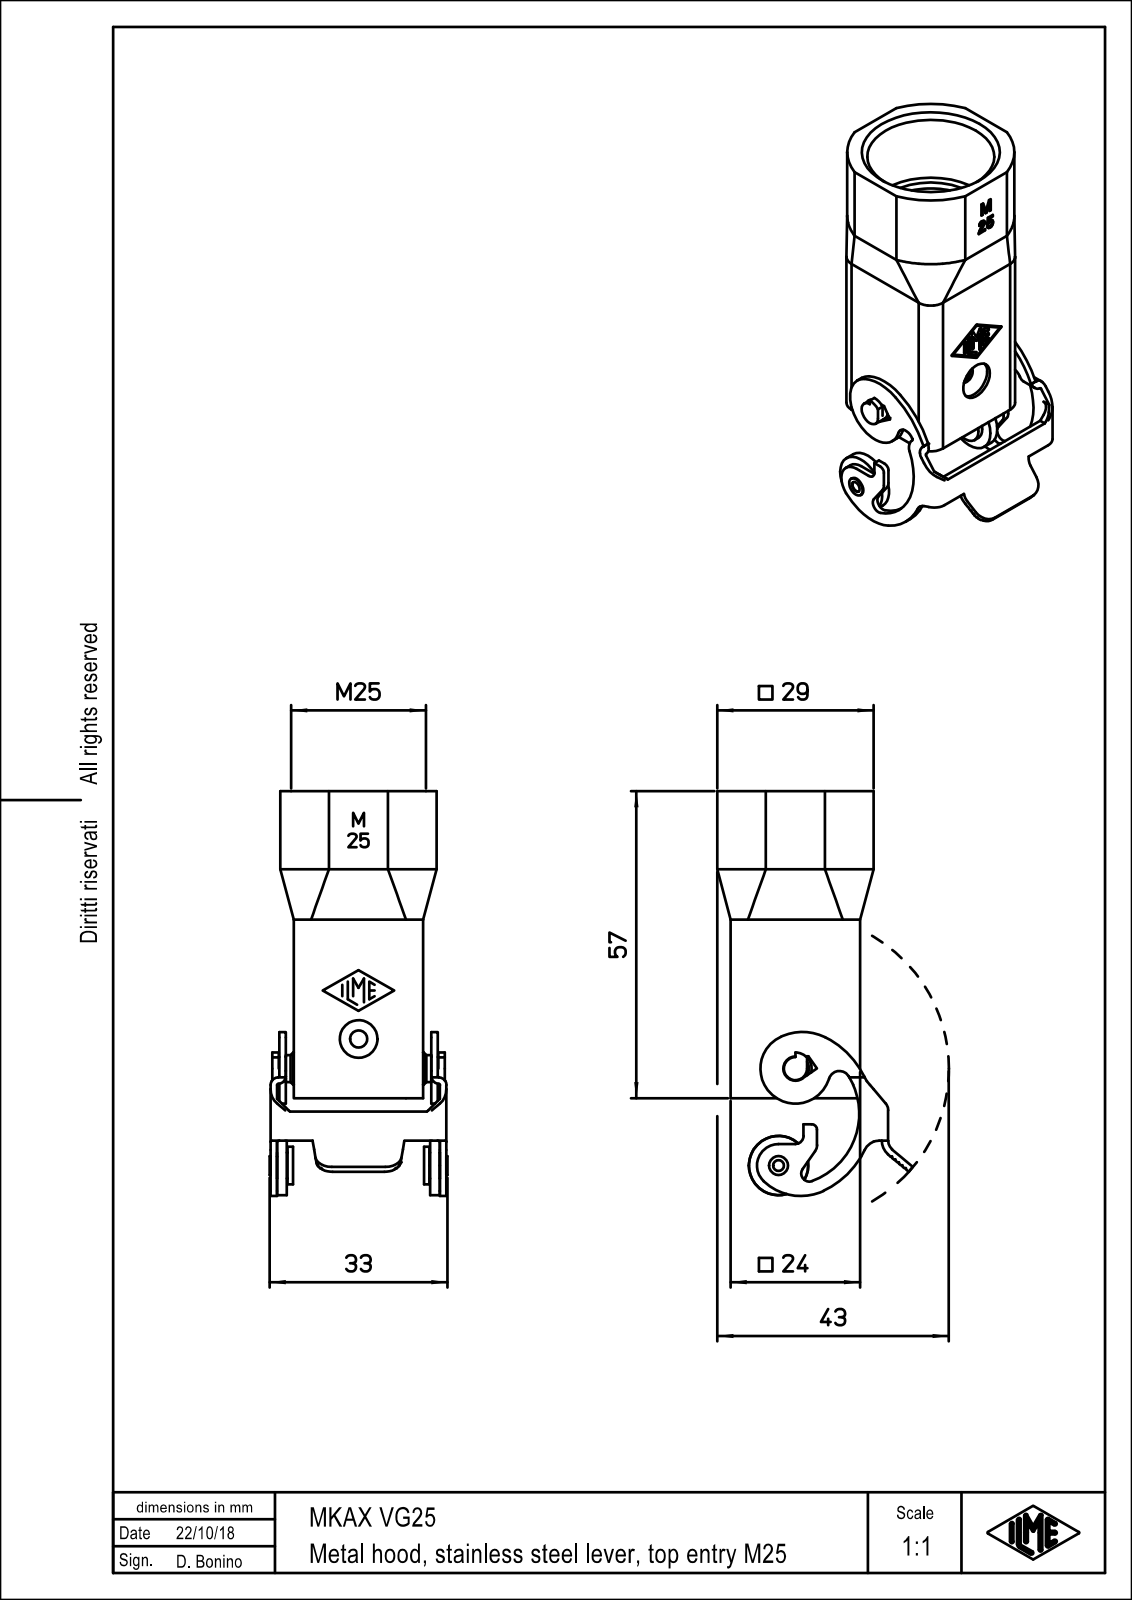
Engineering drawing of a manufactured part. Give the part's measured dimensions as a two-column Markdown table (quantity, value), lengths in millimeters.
| quantity | value |
| --- | --- |
| part name | MKAX_VG25 |
| STEP written by | PTC Creo Elements/Direct Modeling 19.0B 21-Mar-2015 (C) Parametric Technology GmbH (AUTOMOTIVE_DESIGN) |
| units | millimeters |
| bodies | 1 solid, 377 faces (251 planar, 115 cylindrical, 11 other) |
| overall size | 66.13 × 40 × 33 |
| volume | 10 927 mm³ |
| surface area | 13 522 mm² |
| round holes (diameter × count) | 3.2 × 1, 7 × 1, 20 × 1, 25 × 1 |
| round bosses / shafts (diameter × count) | 11 × 1, 7 × 1, 6 × 1, 5 × 1, 4.8 × 1, 4.3 × 1, 3.5 × 1 |
| partial cylindrical surfaces (radius × count) | 0.25 × 15, 2 × 8, 3.2 × 5, 0.2 × 4, 1.4 × 4, 3 × 4, 0.12 × 3, 1.5 × 2 |
| main face-to-face distances | 1.2, 22.8, 21.6, 24, 25.3, 2.5, 3.7, 26.5, 2.7, 25.5 |
